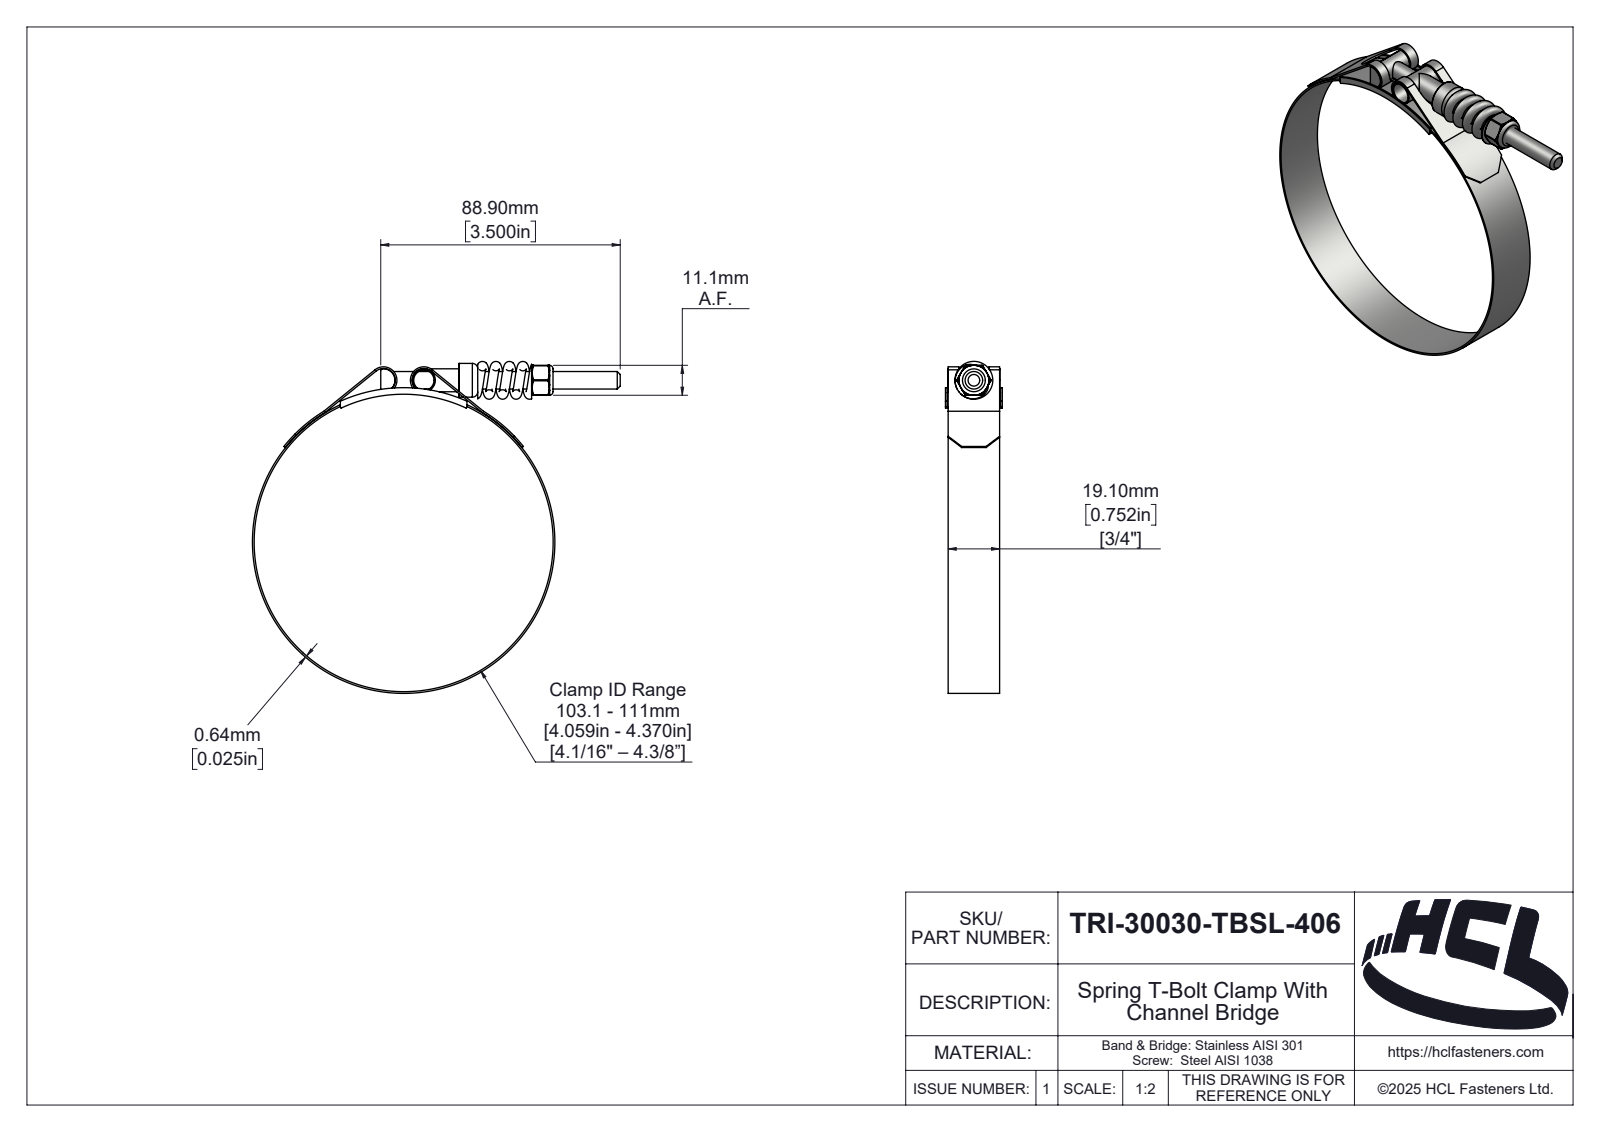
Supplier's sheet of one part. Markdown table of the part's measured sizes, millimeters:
| quantity | value |
| --- | --- |
| part name | TRI-30030-TBSL-406 |
| STEP written by | SolidWorks 2025 (AUTOMOTIVE_DESIGN) |
| units | millimeters |
| bodies | 7 solids, 332 faces (48 planar, 122 cylindrical, 162 other) |
| overall size | 137.54 × 123.2 × 21.1 |
| volume | 12 439 mm³ |
| surface area | 26 118 mm² |
| round holes (diameter × count) | 5.4 × 1, 6.35 × 1, 6.5 × 1, 7.52 × 1, 111 × 1 |
| round bosses / shafts (diameter × count) | 8.52 × 2, 112.28 × 1, 12.52 × 1 |
| partial cylindrical surfaces (radius × count) | 0.39 × 6, 0.5 × 2, 4.36 × 2, 5 × 2, 0.59 × 1, 2.42 × 1, 3.03 × 1, 3.19 × 1 |
| main face-to-face distances | 0.64, 19.1, 1, 20.1, 20.46, 0.36, 19.46, 21.1, 56, 11.11 |
| hole center spacings | 60.5 |
